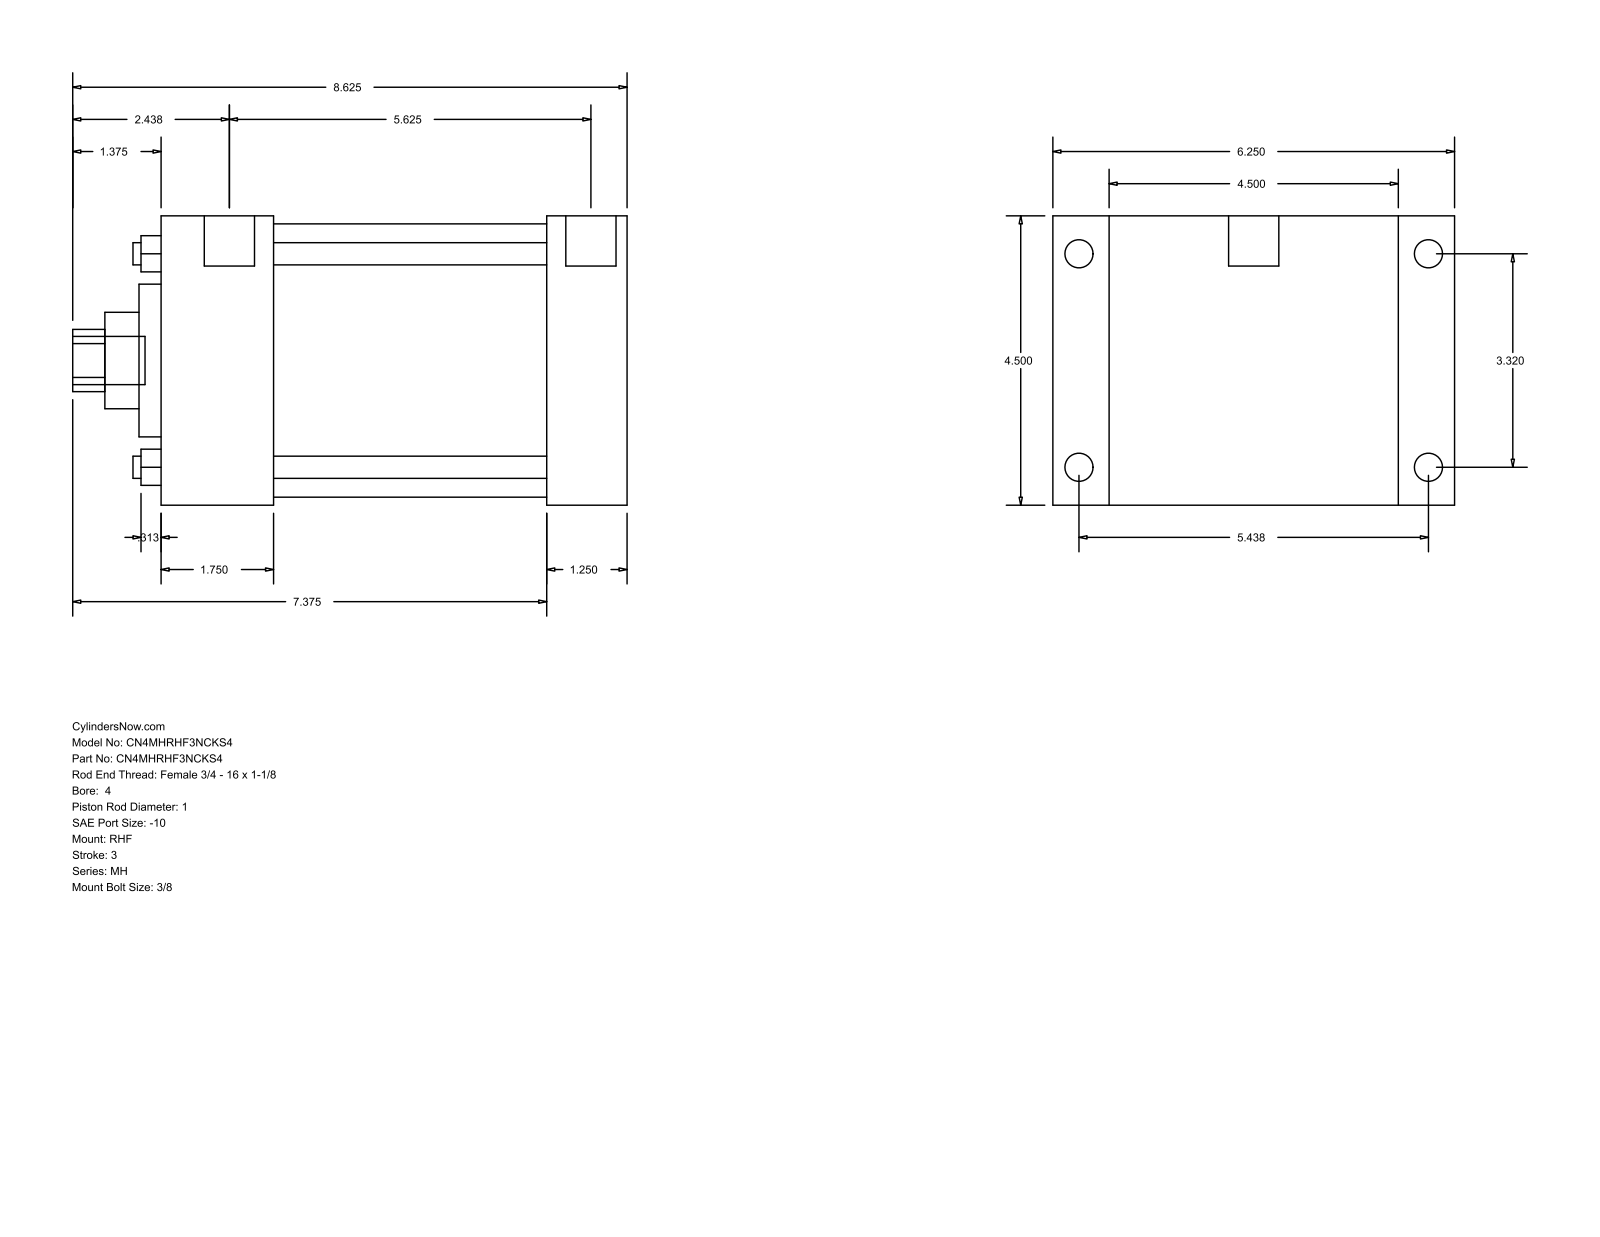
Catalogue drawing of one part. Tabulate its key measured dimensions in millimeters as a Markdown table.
| quantity | value |
| --- | --- |
| part name | MH_RHF__0400_1 |
| STEP written by | GSSL Pune (CONFIG_CONTROL_DESIGN) |
| units | millimeters |
| bodies | 0 solids, 90 faces (61 planar, 29 cylindrical, 0 other) |
| overall size | 219.07 × 158.75 × 114.3 |
| round holes (diameter × count) | 8.76 × 4, 25.4 × 1, 38.1 × 1, 60.33 × 1, 107.95 × 1 |
| round bosses / shafts (diameter × count) | 11.13 × 4, 8.73 × 4, 19.84 × 2, 19.05 × 1 |
| partial cylindrical surfaces (radius × count) | 12.29 × 1 |
| main face-to-face distances | 114.3, 184.15, 152.4, 31.75, 22.23, 136.53, 44.46, 107.94, 139.69, 158.76 |
| hole center spacings | 59.62, 84.32, 119.25 |
